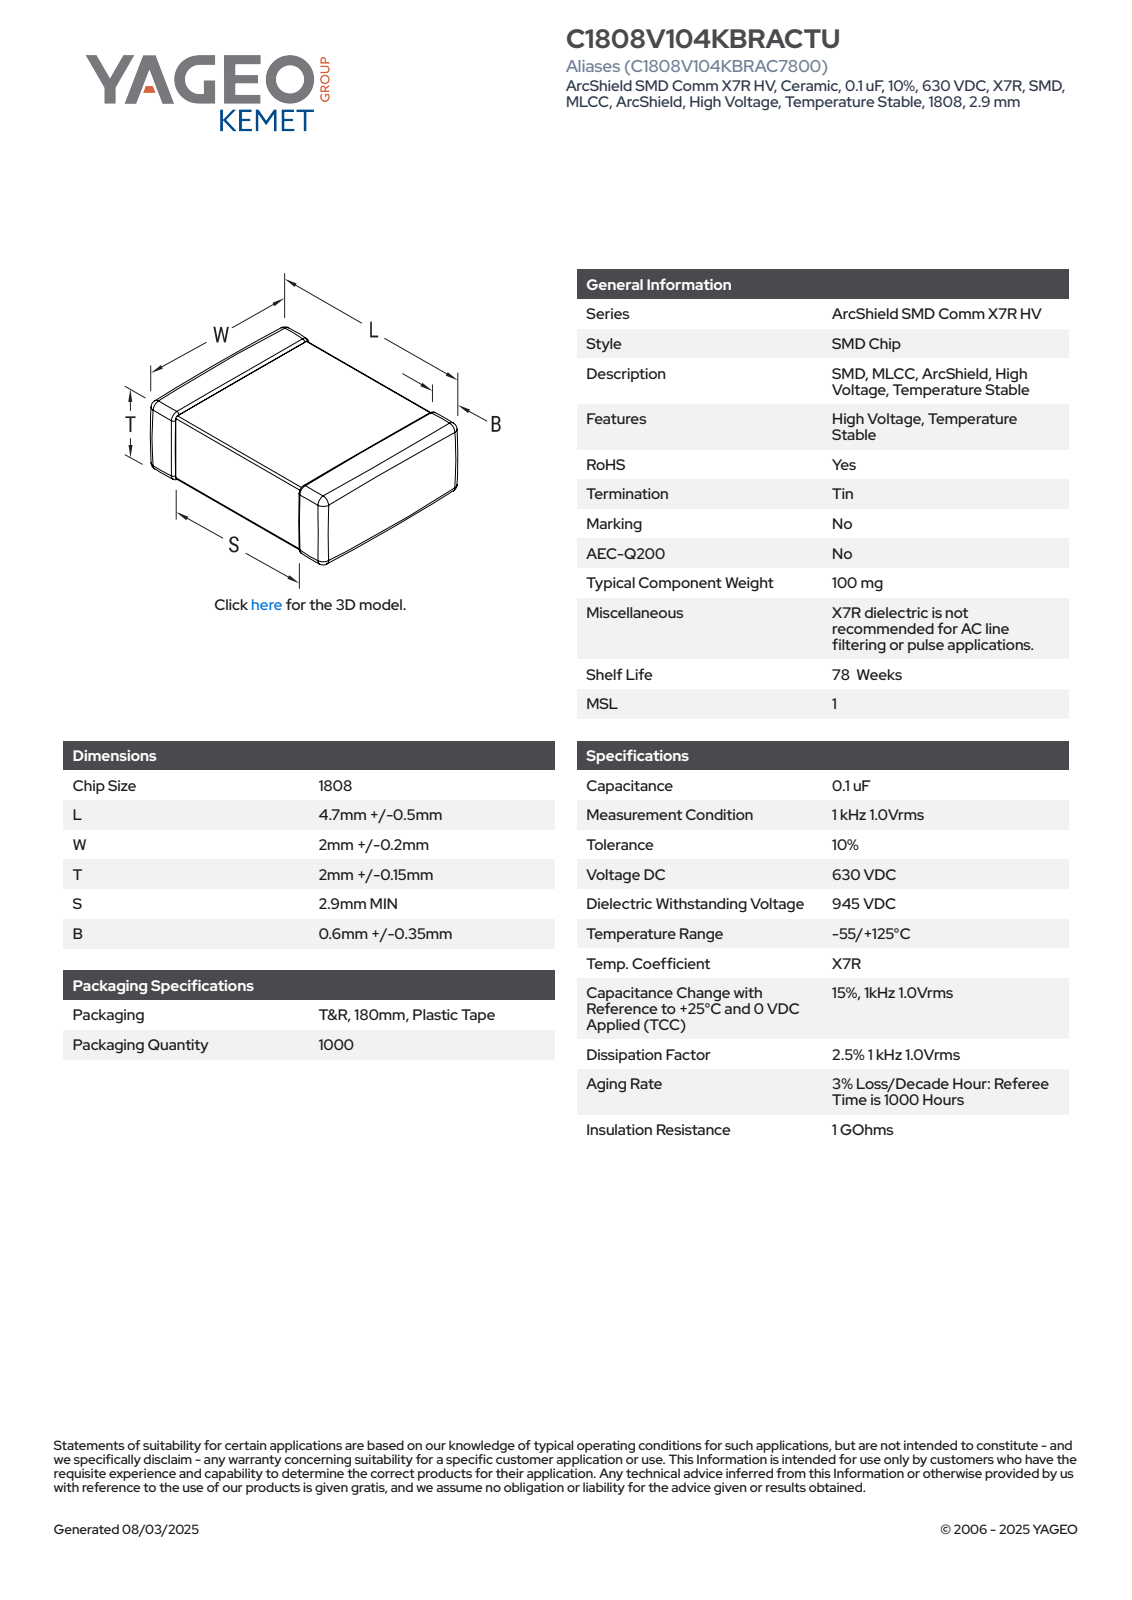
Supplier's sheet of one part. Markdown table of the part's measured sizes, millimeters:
| quantity | value |
| --- | --- |
| part name | CCS_CCSTDNOS_1808_L5.2W2.2T2.15B0.95 |
| STEP written by | SolidWorks 2014 (AUTOMOTIVE_DESIGN) |
| units | millimeters |
| bodies | 4 solids, 125 faces (71 planar, 38 cylindrical, 16 other) |
| overall size | 5.2 × 2.2 × 2.15 |
| volume | 23 mm³ |
| surface area | 54 mm² |
| main face-to-face distances | 2.1, 2.15, 2.05, 5.2, 2.2, 2.11, 2.06, 0.89, 1.26, 0.37 |
